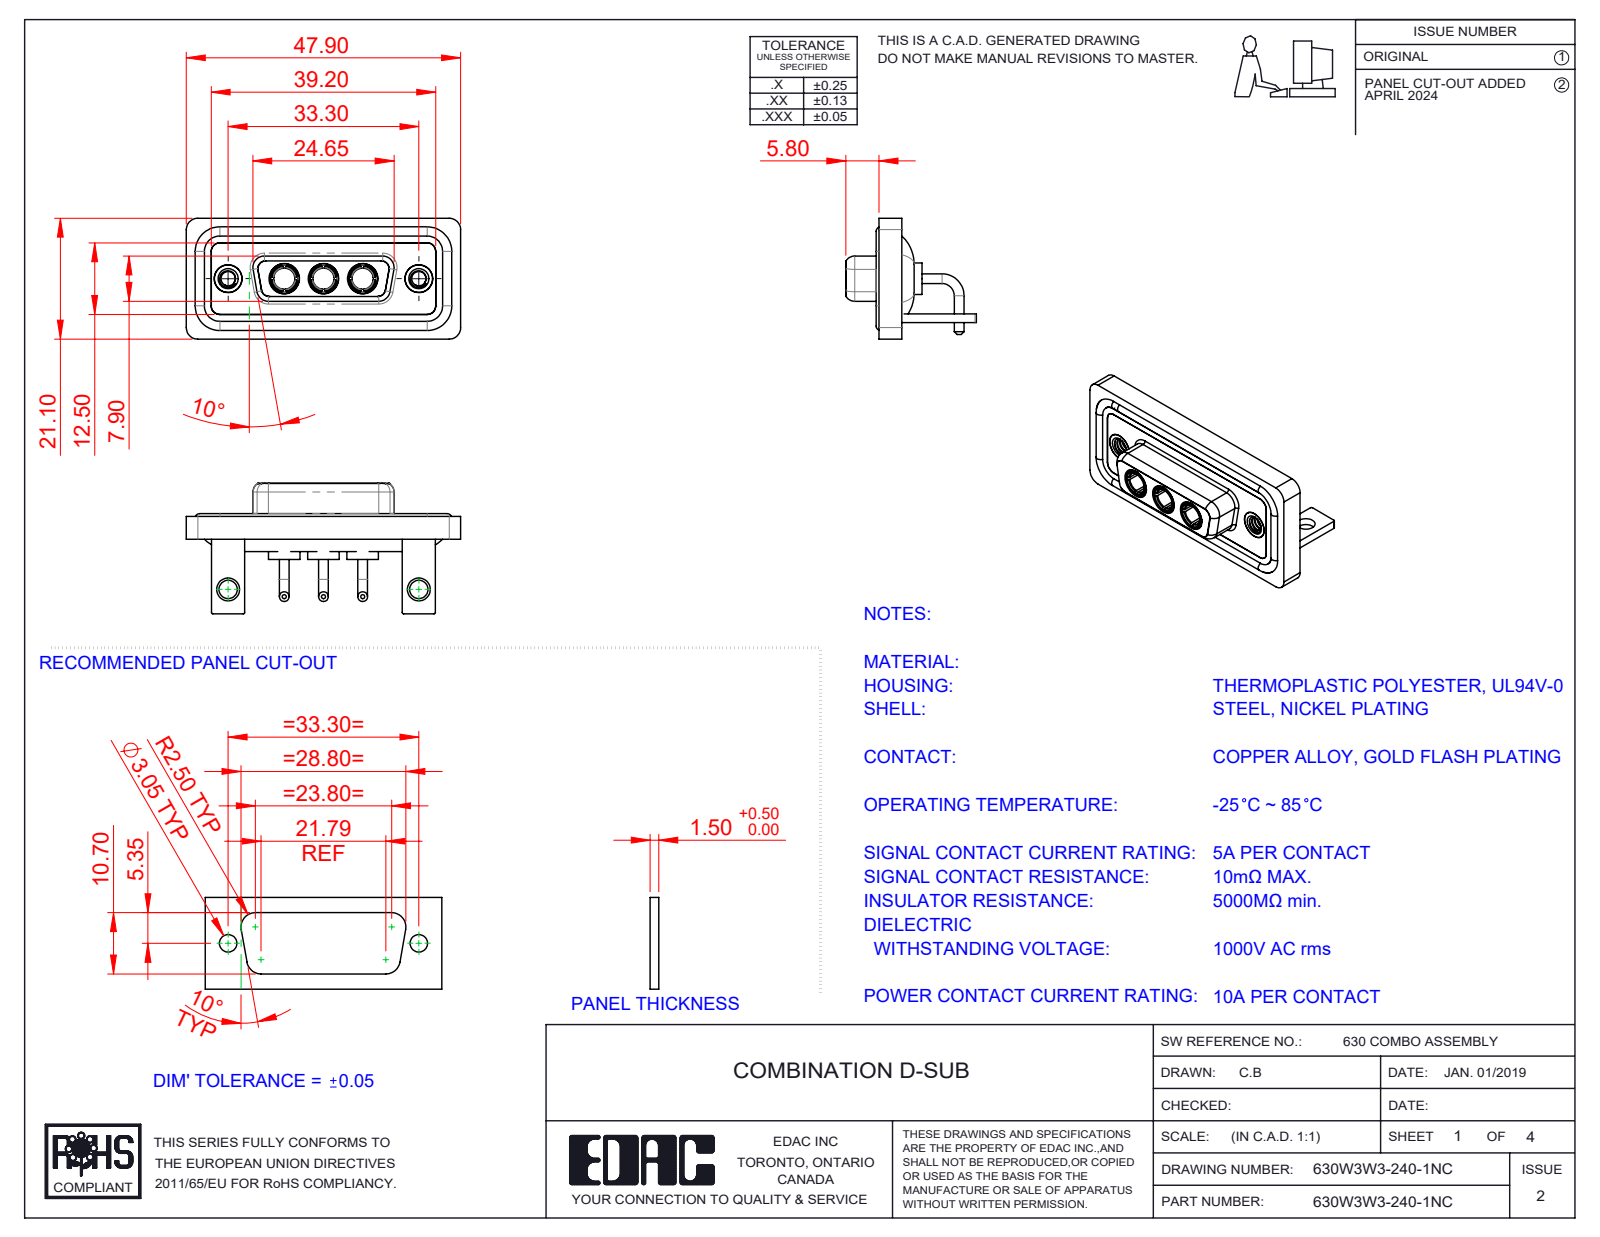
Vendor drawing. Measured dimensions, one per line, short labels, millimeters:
name: 630Combo Waterproof Housing_15 Contacts; 630Combo Threaded Rivet_A; Power Socket_10A RA; 630Combo Shell Front_15 Contacts (+4 more)
written by: SolidWorks 2023 (CONFIG_CONTROL_DESIGN)
unit: mm
bodies: 15 solids, 662 faces (212 planar, 285 cylindrical, 165 other)
size: 47.9 × 22.8 × 21.1
volume: 6 366 mm³; area: 10 558 mm²
holes: 5× ⌀4.85, 3× ⌀3.7, 3× ⌀5.3, 2× ⌀2.5, 2× ⌀3.2, 2× ⌀4, 2× ⌀4.05, 2× ⌀5
bosses: 6× ⌀1.7, 4× ⌀1.6, 3× ⌀5.5, 3× ⌀5.2, 3× ⌀4.96, 3× ⌀4.75, 3× ⌀3.75, 2× ⌀4.95
rounds: 21× R2, 18× R1.5, 16× R0.25, 12× R1.35, 8× R1.6, 5× R0.5, 4× R0.6, 4× R0.65
face distances: 0.4, 2.9, 1.5, 1.8, 3.7, 1.1, 4.1, 1.6, 2.5, 1.4
hole spacings: 6.85, 9.8, 16.65, 23.5, 33.3, 13.7
